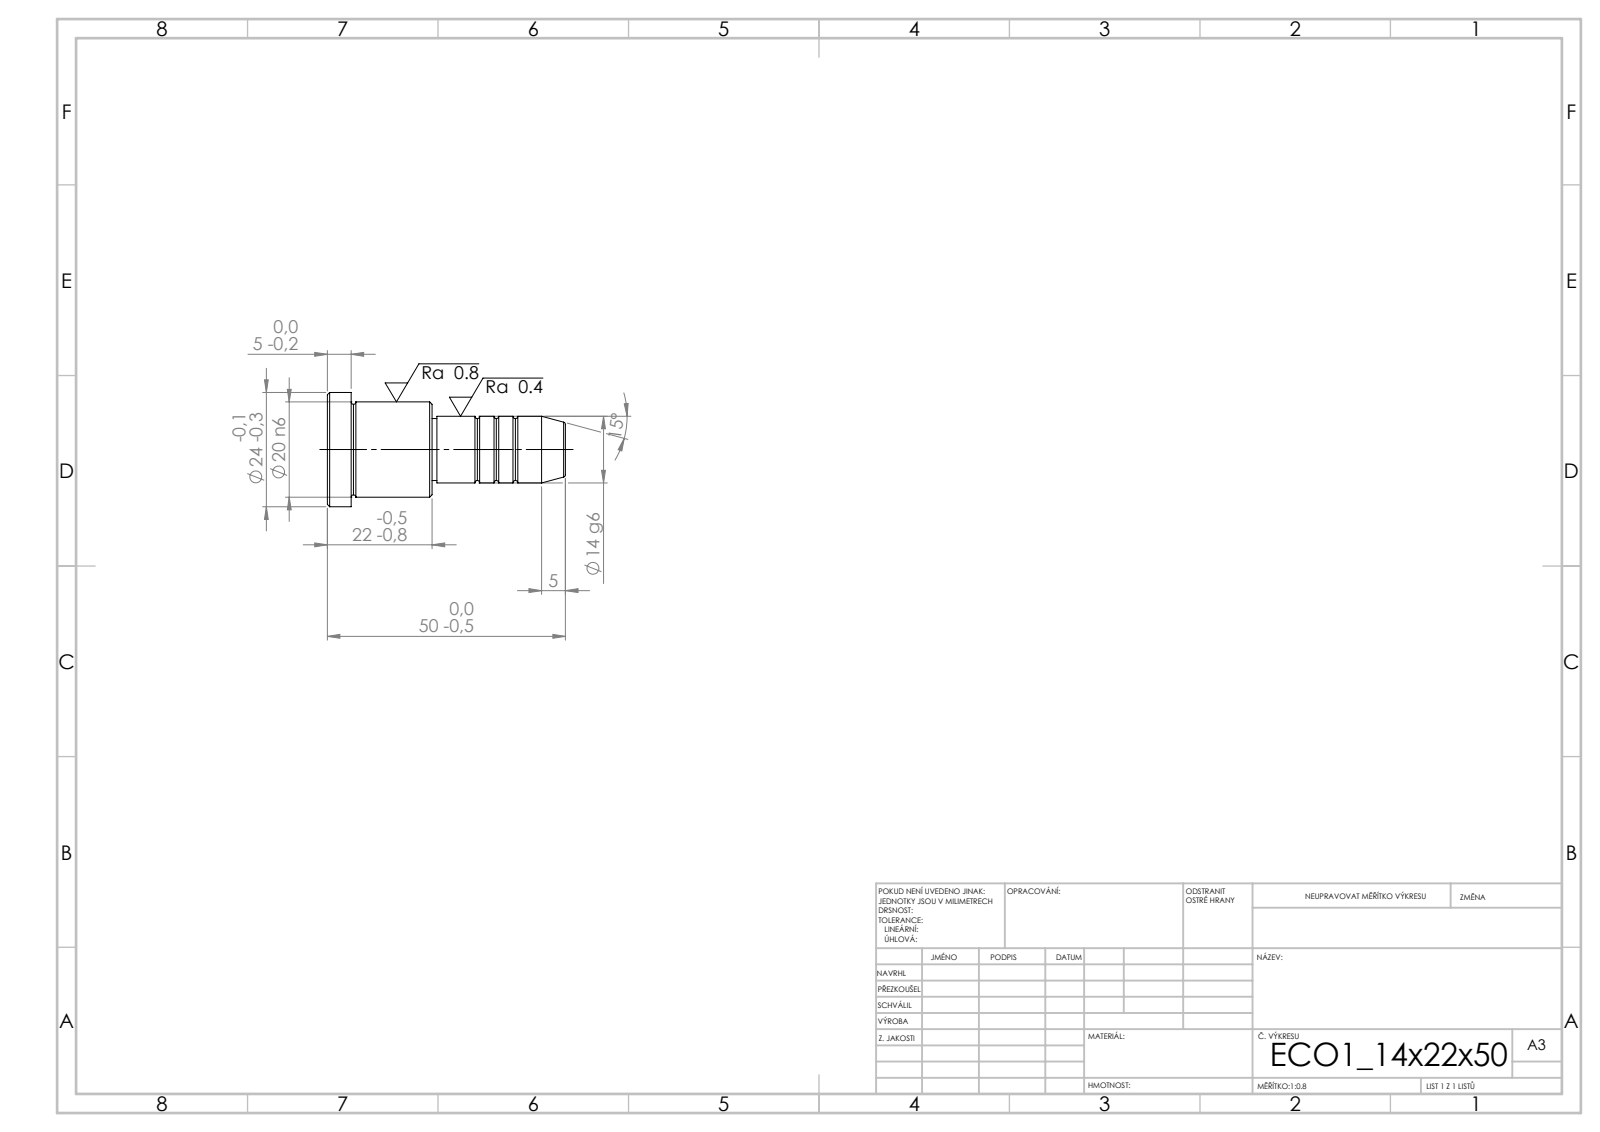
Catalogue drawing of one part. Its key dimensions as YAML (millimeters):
step_written_by: "SolidWorks 2019 (CONFIG_CONTROL_DESIGN)"
units: millimeters
bodies: {solids: 1, faces: 43, planar: 5, cylindrical: 14, other: 24}
overall_size: [50, 24, 24]
volume: 11661
surface_area: 3607
round_bosses_or_shafts:
  - {diameter: 24, count: 1}
  - {diameter: 20, count: 1}
  - {diameter: 14, count: 1}
  - {diameter: 13, count: 1}
face_to_face_distances: [22, 17, 5, 28, 45, 50, 27, 1, 18, 23]
